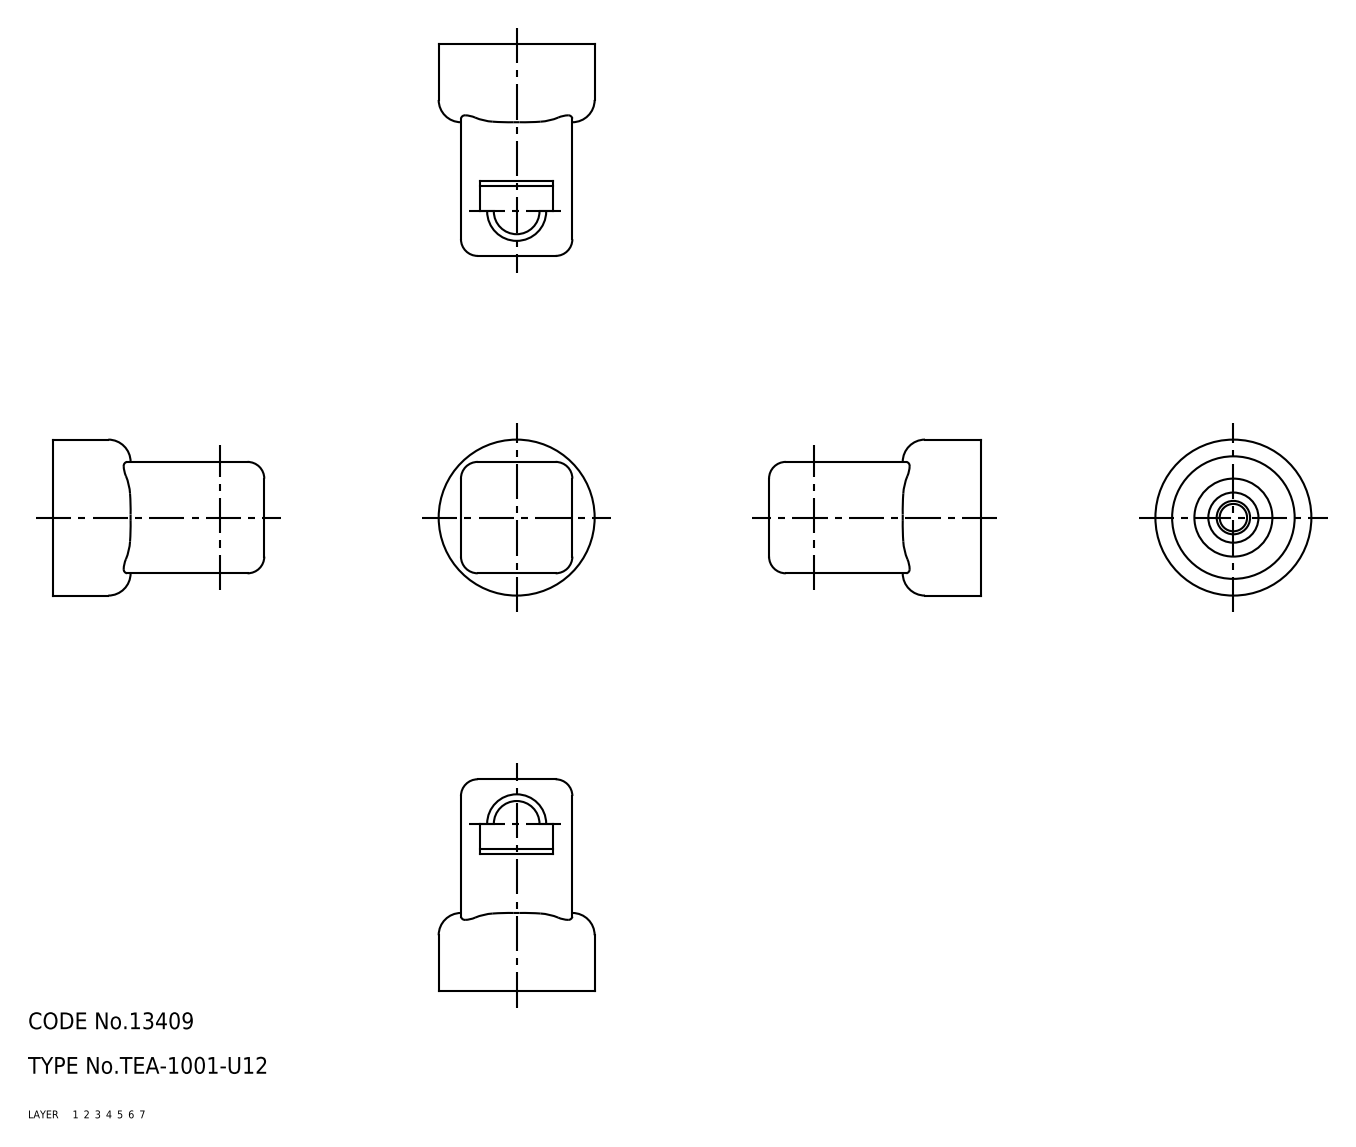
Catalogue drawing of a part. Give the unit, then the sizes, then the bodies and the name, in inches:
Units: inches
Overall size (bounding box): 1.496 × 1.102 × 1.102
Volume: 0.713 in³ · Surface area: 8.399 in²
Bodies: 1 solid, 40 faces (0 planar, 0 cylindrical, 40 other)
Part name (STEP PRODUCT): guide
STEP written by: CADfix (AUTOMOTIVE_DESIGN)
